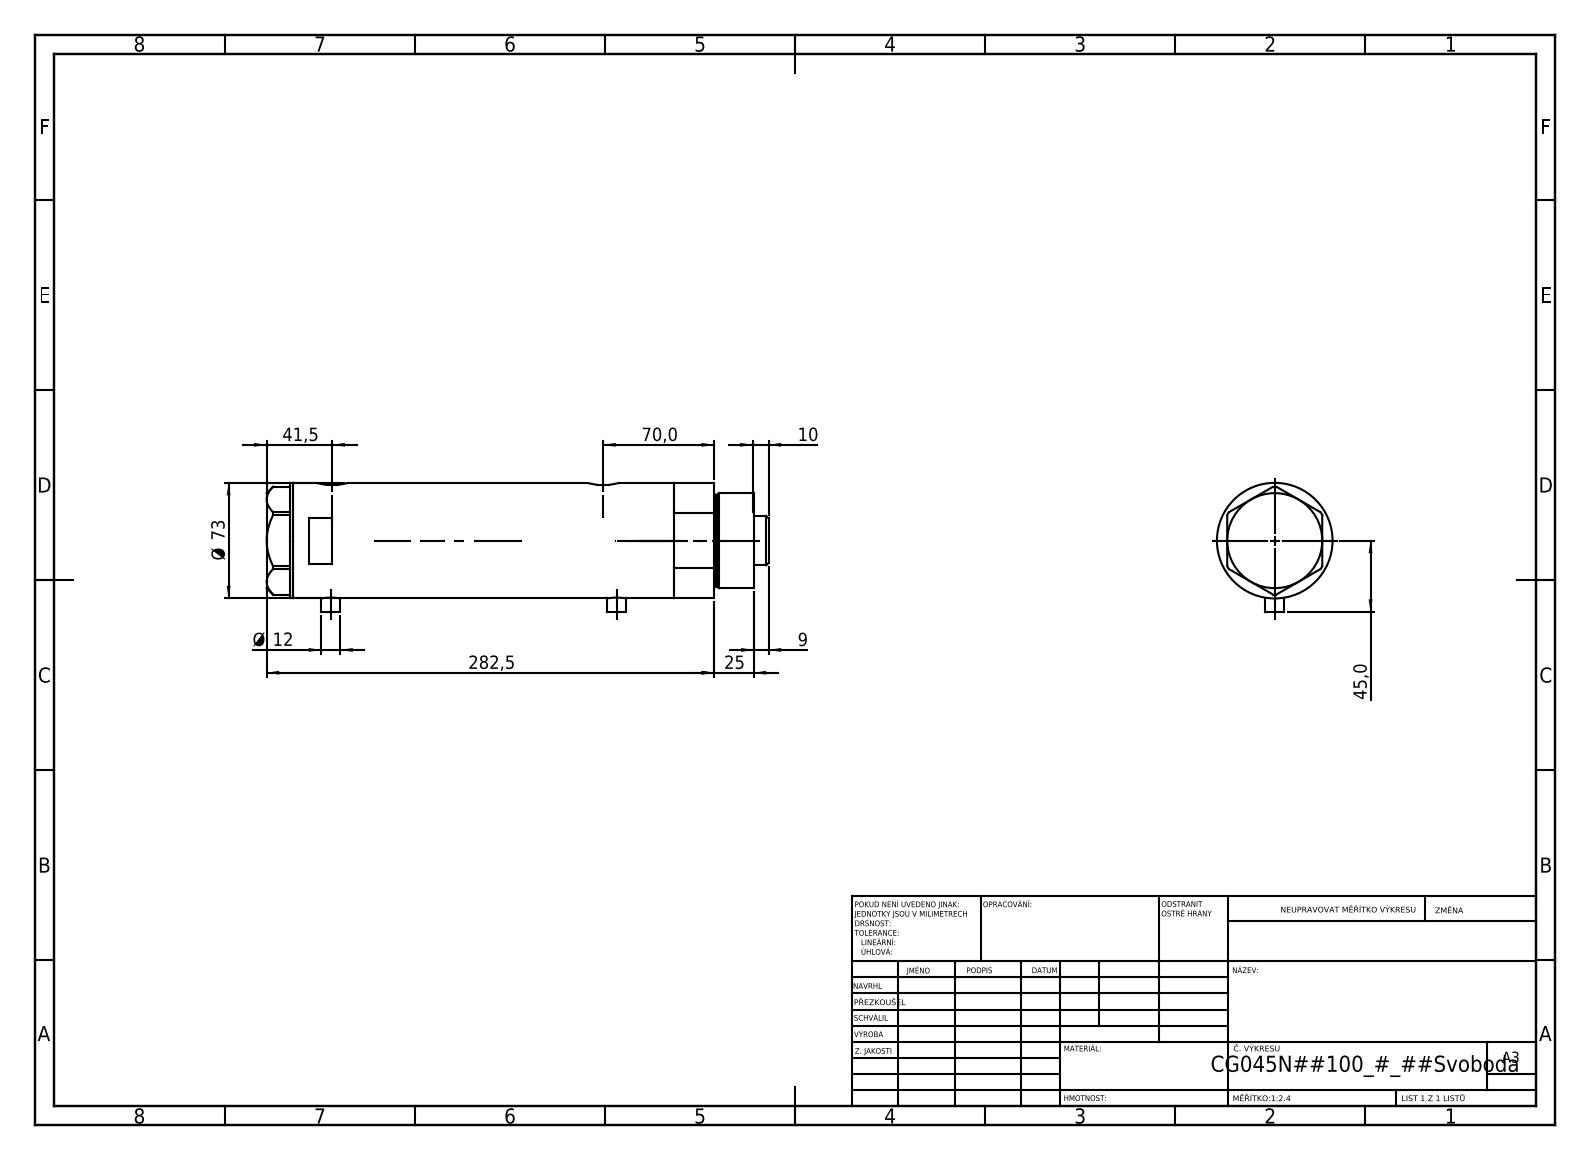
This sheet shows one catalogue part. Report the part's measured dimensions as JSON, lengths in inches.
{"part_name": "V270CG_FRONT; V270CG_VC; V270CG_BACK; V270CG_MIDDLE", "step_written_by": "SolidWorks 2019 (CONFIG_CONTROL_DESIGN)", "units": "inches", "bodies": {"solids": 4, "faces": 125, "planar": 50, "cylindrical": 55, "other": 20}, "overall_size": [12.476, 3.209, 2.874], "volume_in3": 70.24, "surface_area_in2": 286.2, "round_holes": [[0.197, 2], [0.492, 2], [0.518, 2], [0.413, 1], [1.26, 1], [1.319, 1], [1.772, 1], [1.89, 1], [2.52, 1]], "round_bosses_or_shafts": [[0.472, 2], [2.874, 1], [2.362, 1], [2.283, 1], [1.22, 1]], "partial_cylinders_radius": [[0.394, 2]], "face_to_face_distances": [7.717, 1.024, 6.693, 0.65, 1.673, 8.366, 0.079, 11.457, 12.106, 10.433], "hole_center_spacings": [0.039, 0.335, 6.732, 6.772, 7.067, 7.106]}
